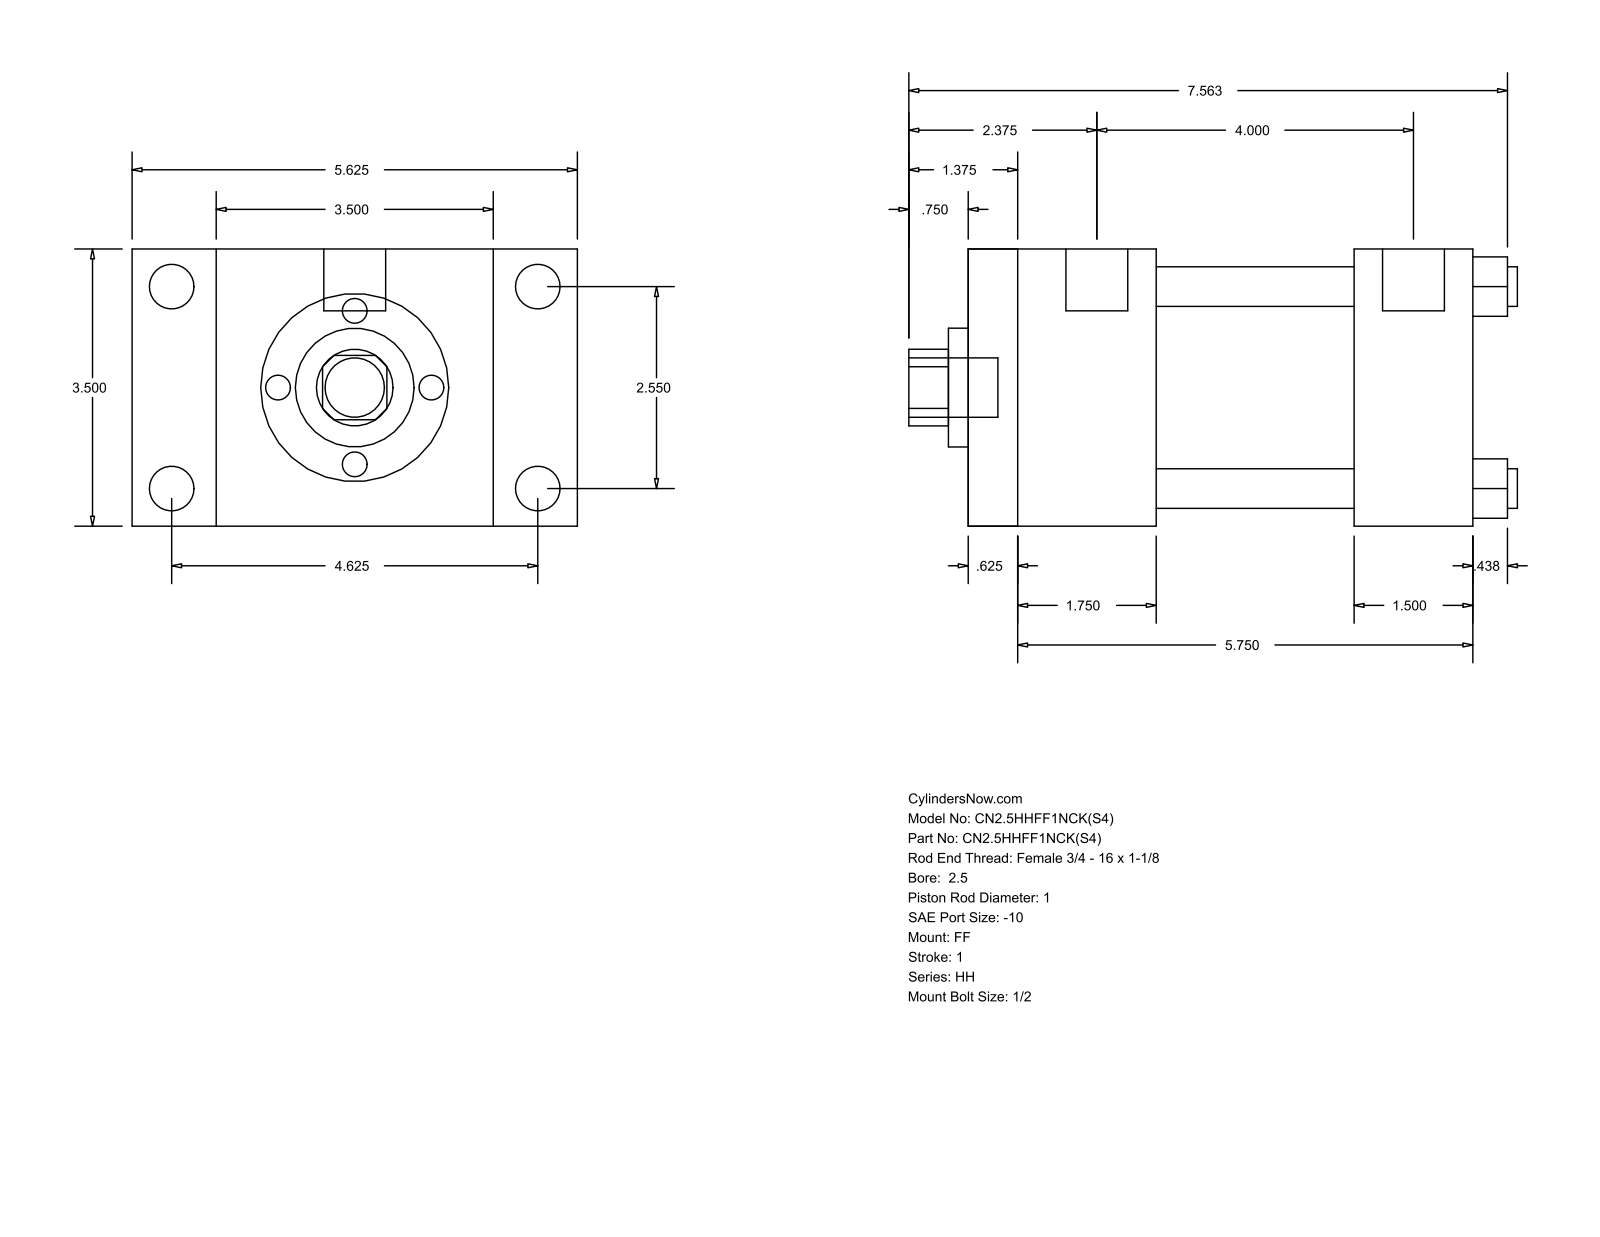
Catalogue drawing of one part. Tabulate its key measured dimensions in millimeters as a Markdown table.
| quantity | value |
| --- | --- |
| part name | HH_FF__0250_1 |
| STEP written by | GSSL Pune (CONFIG_CONTROL_DESIGN) |
| units | millimeters |
| bodies | 0 solids, 92 faces (64 planar, 28 cylindrical, 0 other) |
| overall size | 195.26 × 142.88 × 88.9 |
| round holes (diameter × count) | 12.7 × 4, 25.4 × 1, 38.1 × 1, 73.03 × 1 |
| round bosses / shafts (diameter × count) | 14.3 × 4, 5.56 × 4, 19.84 × 2, 19.05 × 1 |
| partial cylindrical surfaces (radius × count) | 12.29 × 1 |
| main face-to-face distances | 88.9, 161.92, 15.87, 146.05, 60.33, 44.46, 101.59, 123.83, 107.96, 63.5 |
| hole center spacings | 45.79, 64.76, 91.58 |
